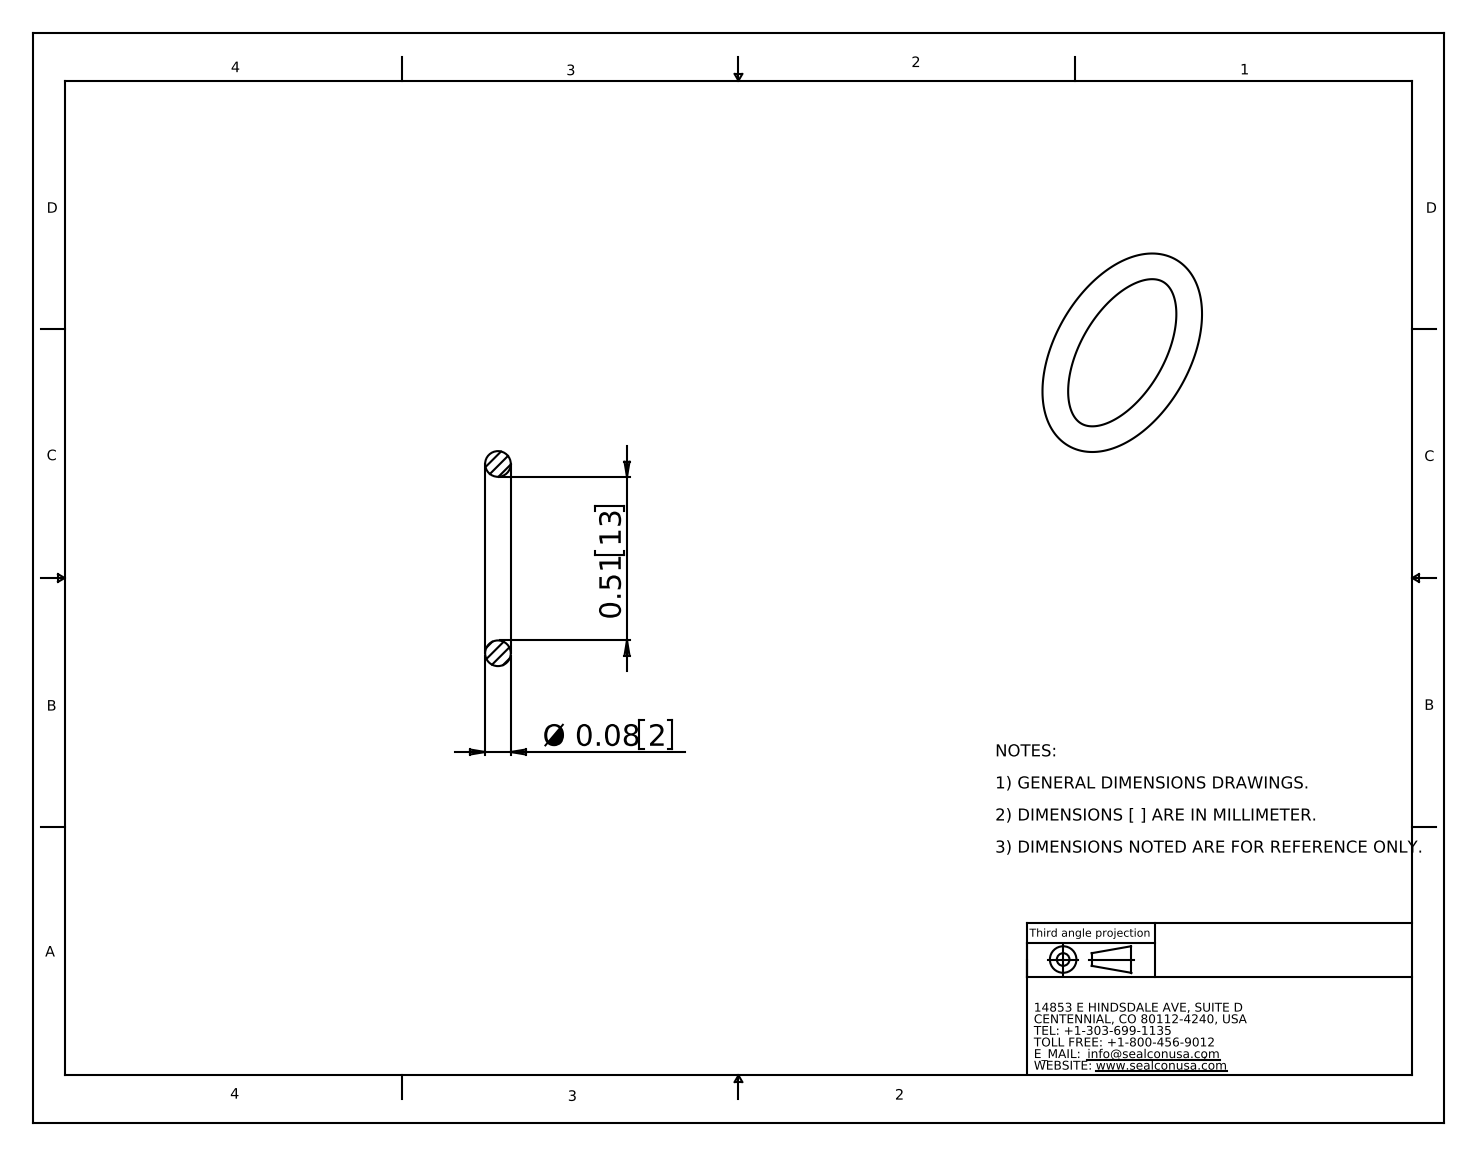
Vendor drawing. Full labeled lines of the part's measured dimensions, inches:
Part name (STEP PRODUCT): OR-38-SI
STEP written by: SolidWorks 2008 (CONFIG_CONTROL_DESIGN)
Units: inches
Bodies: 1 solid, 4 faces (0 planar, 0 cylindrical, 4 other)
Overall size (bounding box): 0.67 × 0.67 × 0.08
Volume: 0.009 in³ · Surface area: 0.466 in²
